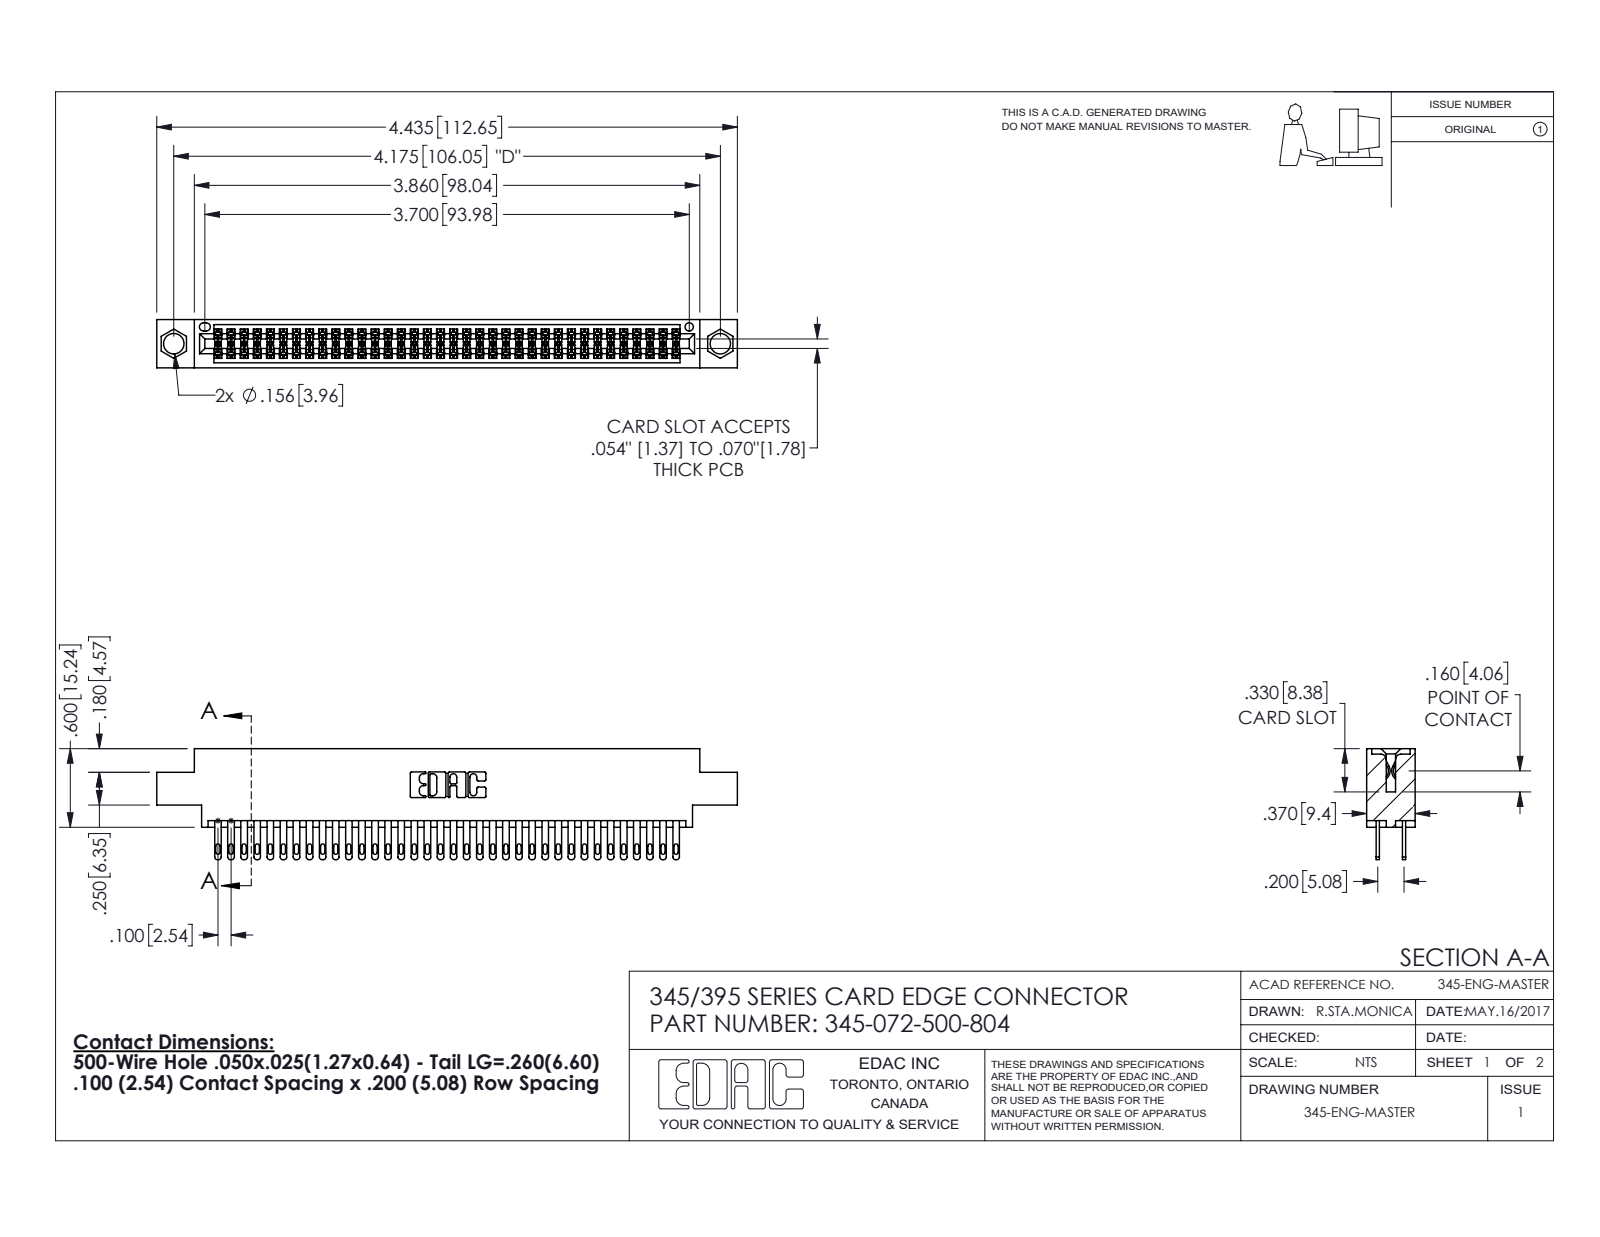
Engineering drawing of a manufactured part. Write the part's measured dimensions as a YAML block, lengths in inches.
part_name: "345-292-001_345-293-100; 345-072-500-804; 345 Part_0.170 Offset - 0.156 Dia-TI"
step_written_by: "SolidWorks 2020 (CONFIG_CONTROL_DESIGN)"
units: inches
bodies: {solids: 73, faces: 3456, planar: 2042, cylindrical: 1414, other: 0}
overall_size: [4.435, 0.847, 0.37]
volume: 0.664
surface_area: 25.9
round_holes:
  - {diameter: 0.156, count: 2}
  - {diameter: 0.064, count: 1}
partial_cylinders:
  - {radius: 0.006, count: 108}
  - {radius: 0.016, count: 72}
  - {radius: 0.02, count: 72}
  - {radius: 0.01, count: 22}
  - {radius: 0.007, count: 6}
  - {radius: 0.031, count: 6}
  - {radius: 0.026, count: 3}
  - {radius: 0.014, count: 2}
face_to_face_distances: [0.072, 0.298, 0.2, 0.098, 0.272, 0.025, 0.37, 0.225, 0.175, 0.149]
hole_center_spacings: [0.27, 3.939, 4.175]
